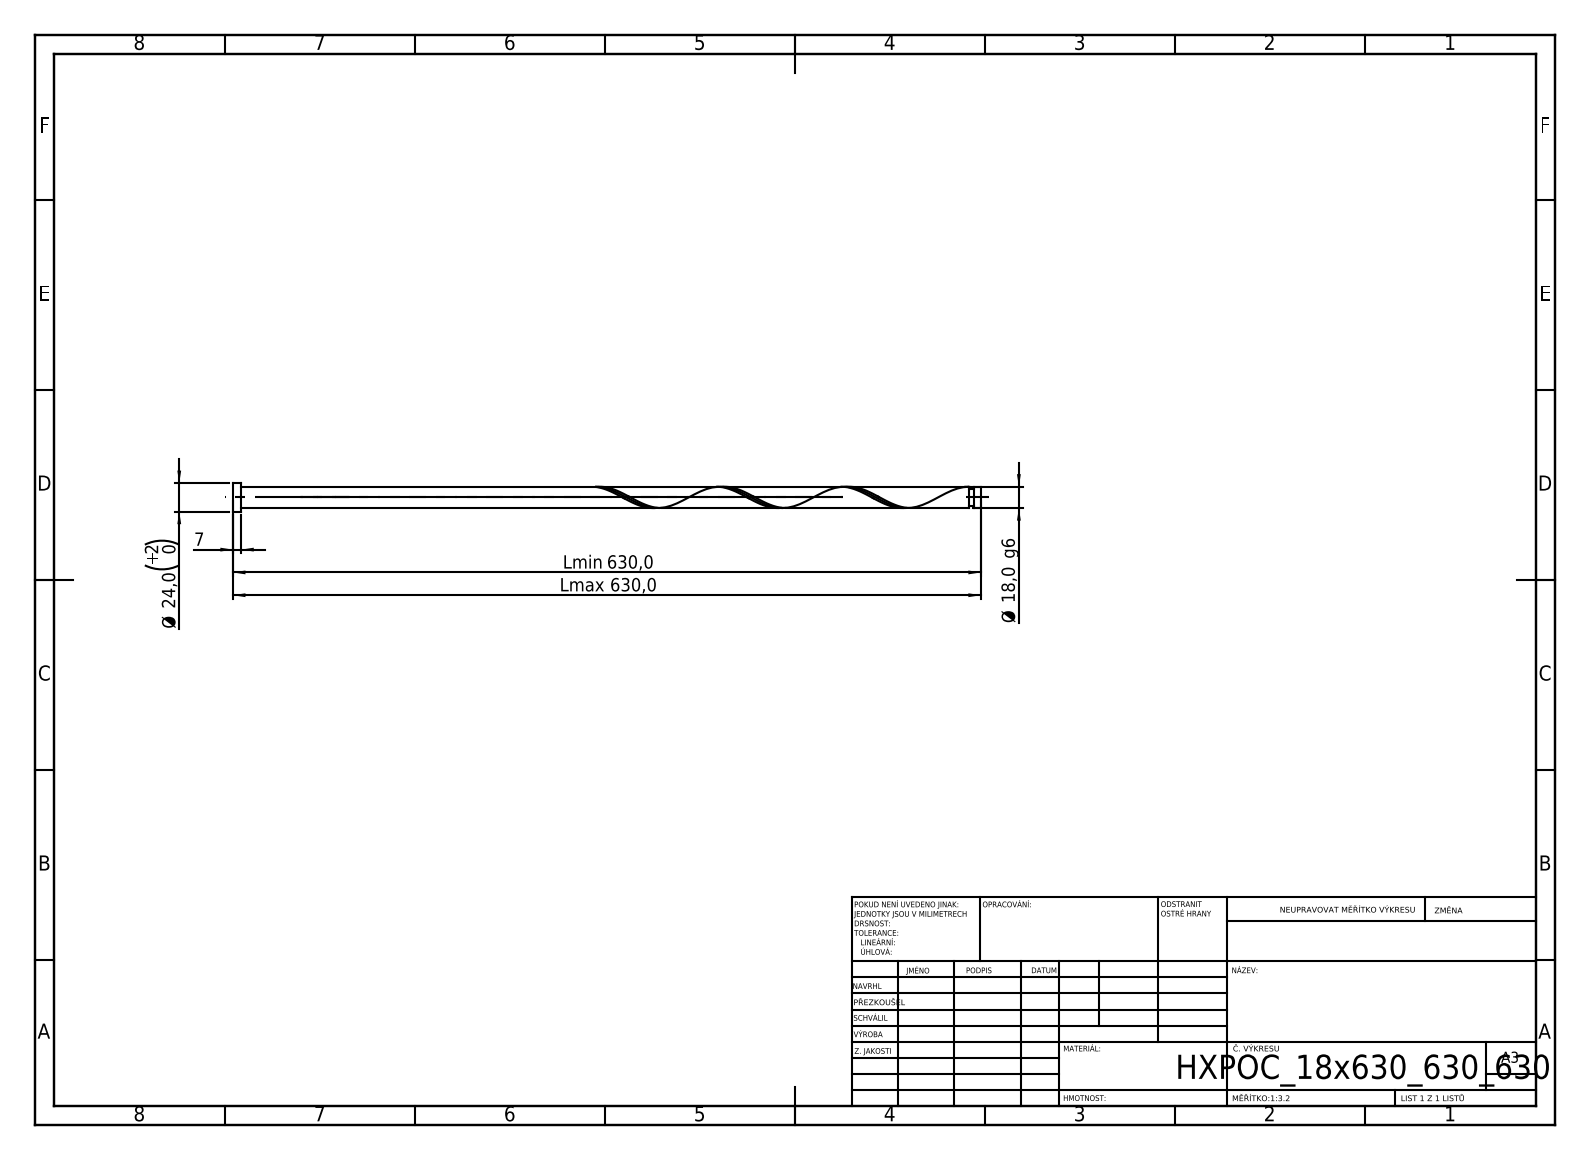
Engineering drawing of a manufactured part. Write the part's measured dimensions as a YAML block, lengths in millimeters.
step_written_by: "SolidWorks 2019 (CONFIG_CONTROL_DESIGN)"
units: millimeters
bodies: {solids: 1, faces: 21, planar: 6, cylindrical: 14, other: 1}
overall_size: [630, 24, 24]
volume: 159836
surface_area: 37444
round_bosses_or_shafts:
  - {diameter: 24, count: 1}
  - {diameter: 18, count: 1}
  - {diameter: 14.4, count: 1}
face_to_face_distances: [630, 7, 623, 623.77, 616.77, 6.23, 620.17, 613.17, 3.6, 9.83]
